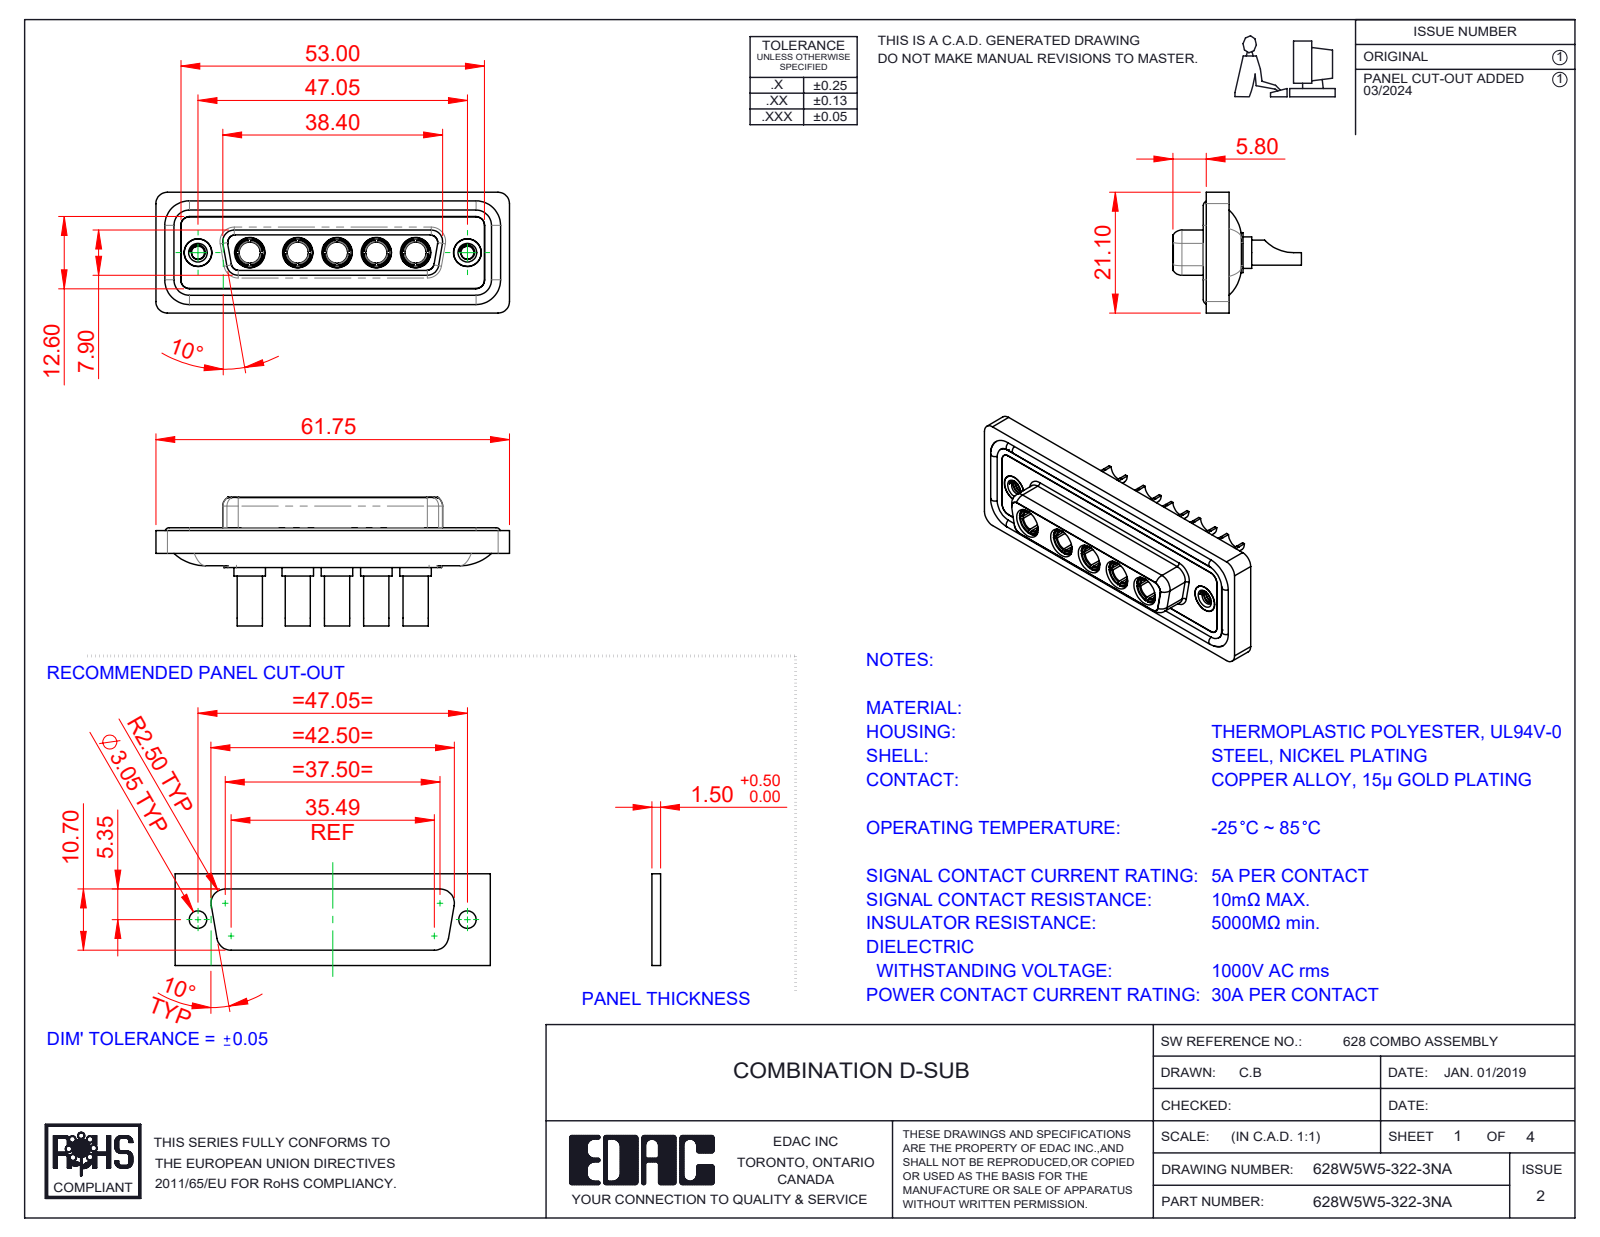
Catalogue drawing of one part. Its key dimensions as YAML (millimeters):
part_name: "628Combo Shell Rear_25 Contacts; 628Combo Waterproof Housing_25 Contacts; 628Combo Threaded Rivet_A; 628Combo Shell Front_25 Contacts (+3 more)"
step_written_by: "SolidWorks 2023 (CONFIG_CONTROL_DESIGN)"
units: millimeters
bodies: {solids: 17, faces: 784, planar: 265, cylindrical: 320, other: 199}
overall_size: [61.75, 22.45, 21.1]
volume: 8294
surface_area: 13951
round_holes:
  - {diameter: 4.85, count: 7}
  - {diameter: 3.5, count: 5}
  - {diameter: 3.7, count: 5}
  - {diameter: 5.3, count: 5}
  - {diameter: 2.26, count: 2}
  - {diameter: 4, count: 2}
  - {diameter: 4.05, count: 2}
  - {diameter: 5, count: 2}
round_bosses_or_shafts:
  - {diameter: 5.5, count: 5}
  - {diameter: 5.2, count: 5}
  - {diameter: 4.96, count: 5}
  - {diameter: 4.75, count: 5}
  - {diameter: 4.4, count: 5}
  - {diameter: 3.75, count: 5}
  - {diameter: 1.6, count: 4}
  - {diameter: 4.95, count: 2}
partial_cylinders:
  - {radius: 1.5, count: 22}
  - {radius: 2, count: 18}
  - {radius: 1.35, count: 8}
  - {radius: 1.6, count: 8}
  - {radius: 2.1, count: 5}
  - {radius: 0.25, count: 4}
  - {radius: 0.5, count: 4}
  - {radius: 0.6, count: 4}
face_to_face_distances: [0.4, 1.8, 7.45, 5.65, 0.5, 7.05, 6.6, 1.6, 1.1, 2.9]
hole_center_spacings: [6.86, 9.04, 13.72, 38.01, 8.39, 15.25, 15.9, 17.43]
